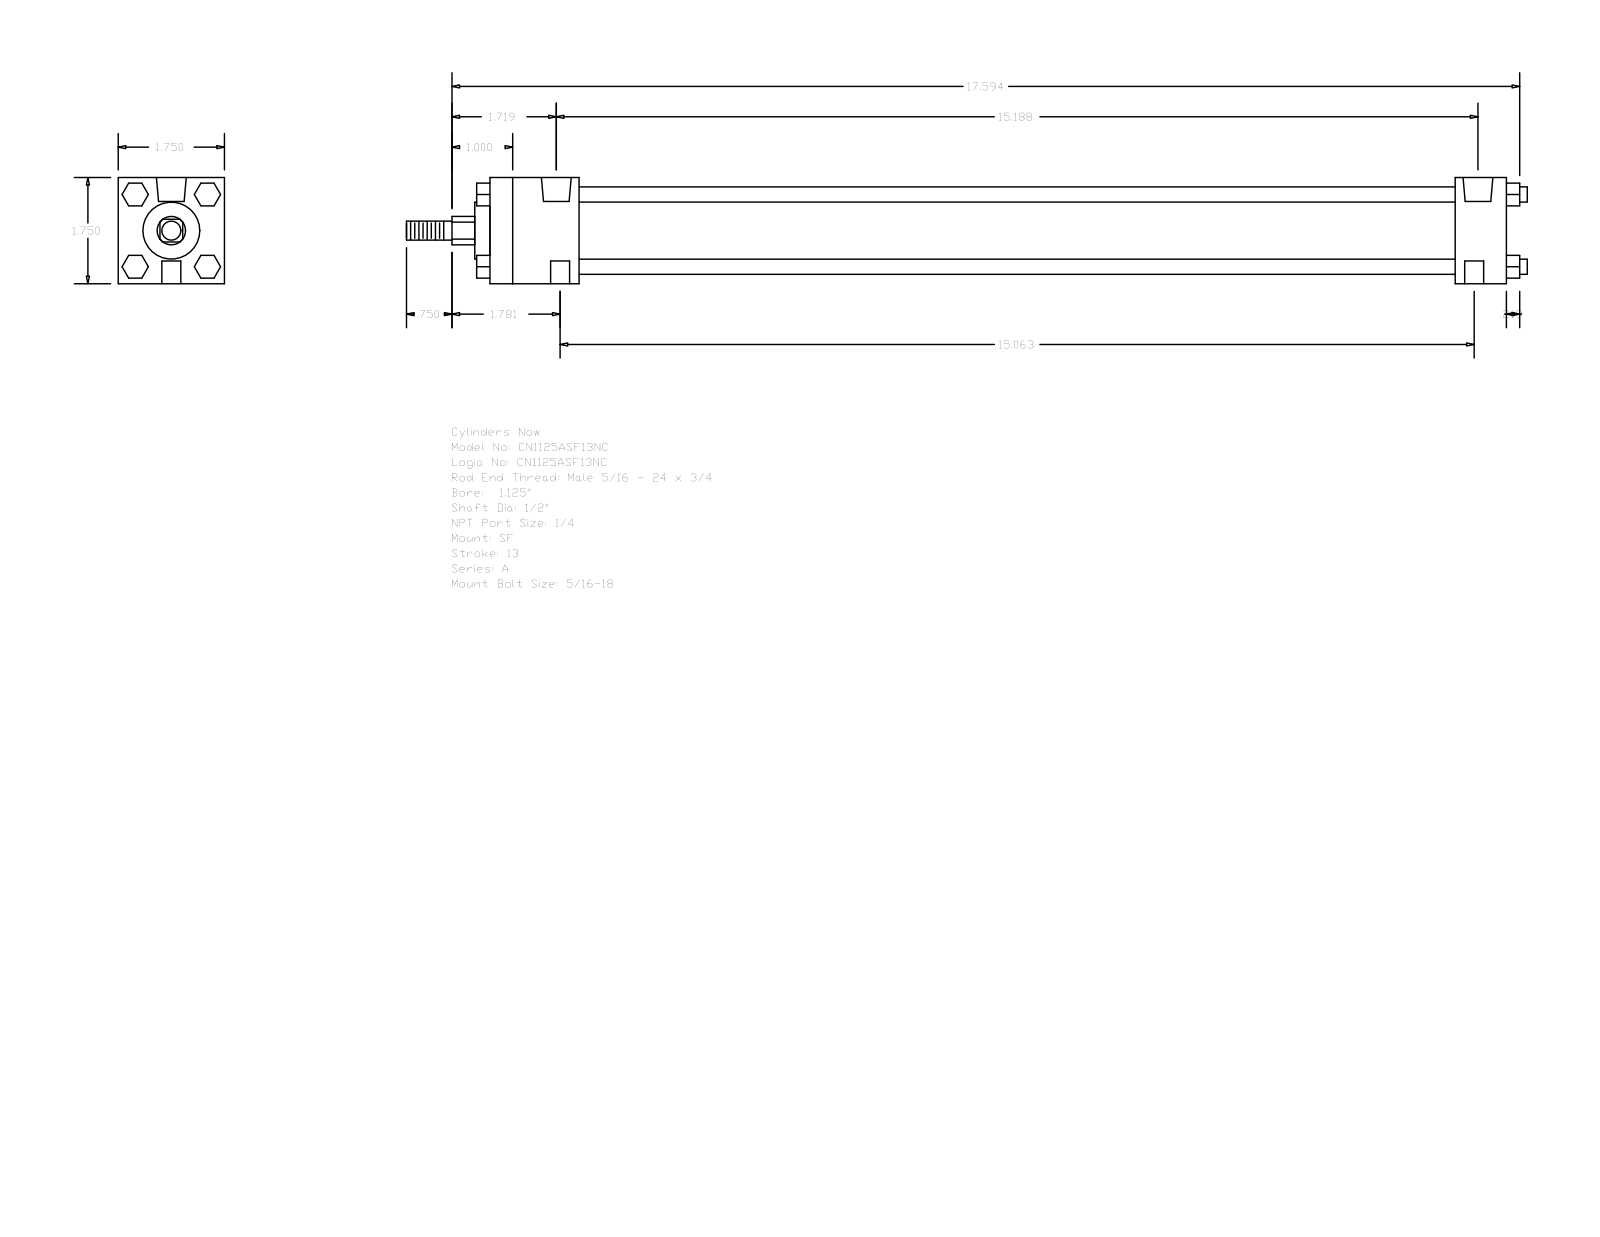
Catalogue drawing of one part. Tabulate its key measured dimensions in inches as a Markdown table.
| quantity | value |
| --- | --- |
| part name | A_SF__0112_0.5 |
| STEP written by | GSSL Pune (CONFIG_CONTROL_DESIGN) |
| units | inches |
| bodies | 0 solids, 120 faces (92 planar, 28 cylindrical, 0 other) |
| overall size | 18.469 × 1.75 × 1.75 |
| round holes (diameter × count) | 0.219 × 2, 0.313 × 2, 0.492 × 2 |
| round bosses / shafts (diameter × count) | 0.25 × 4, 1.255 × 1, 0.937 × 1, 0.5 × 1, 0.313 × 1 |
| partial cylindrical surfaces (radius × count) | 0.234 × 1 |
| main face-to-face distances | 1.75, 16.75, 15.906, 0.844, 1.469, 14.437, 15.281, 0.375, 0.22, 0.219 |
| hole center spacings | 15.063, 0.062, 0.063, 15.125, 15.125, 15.187 |
